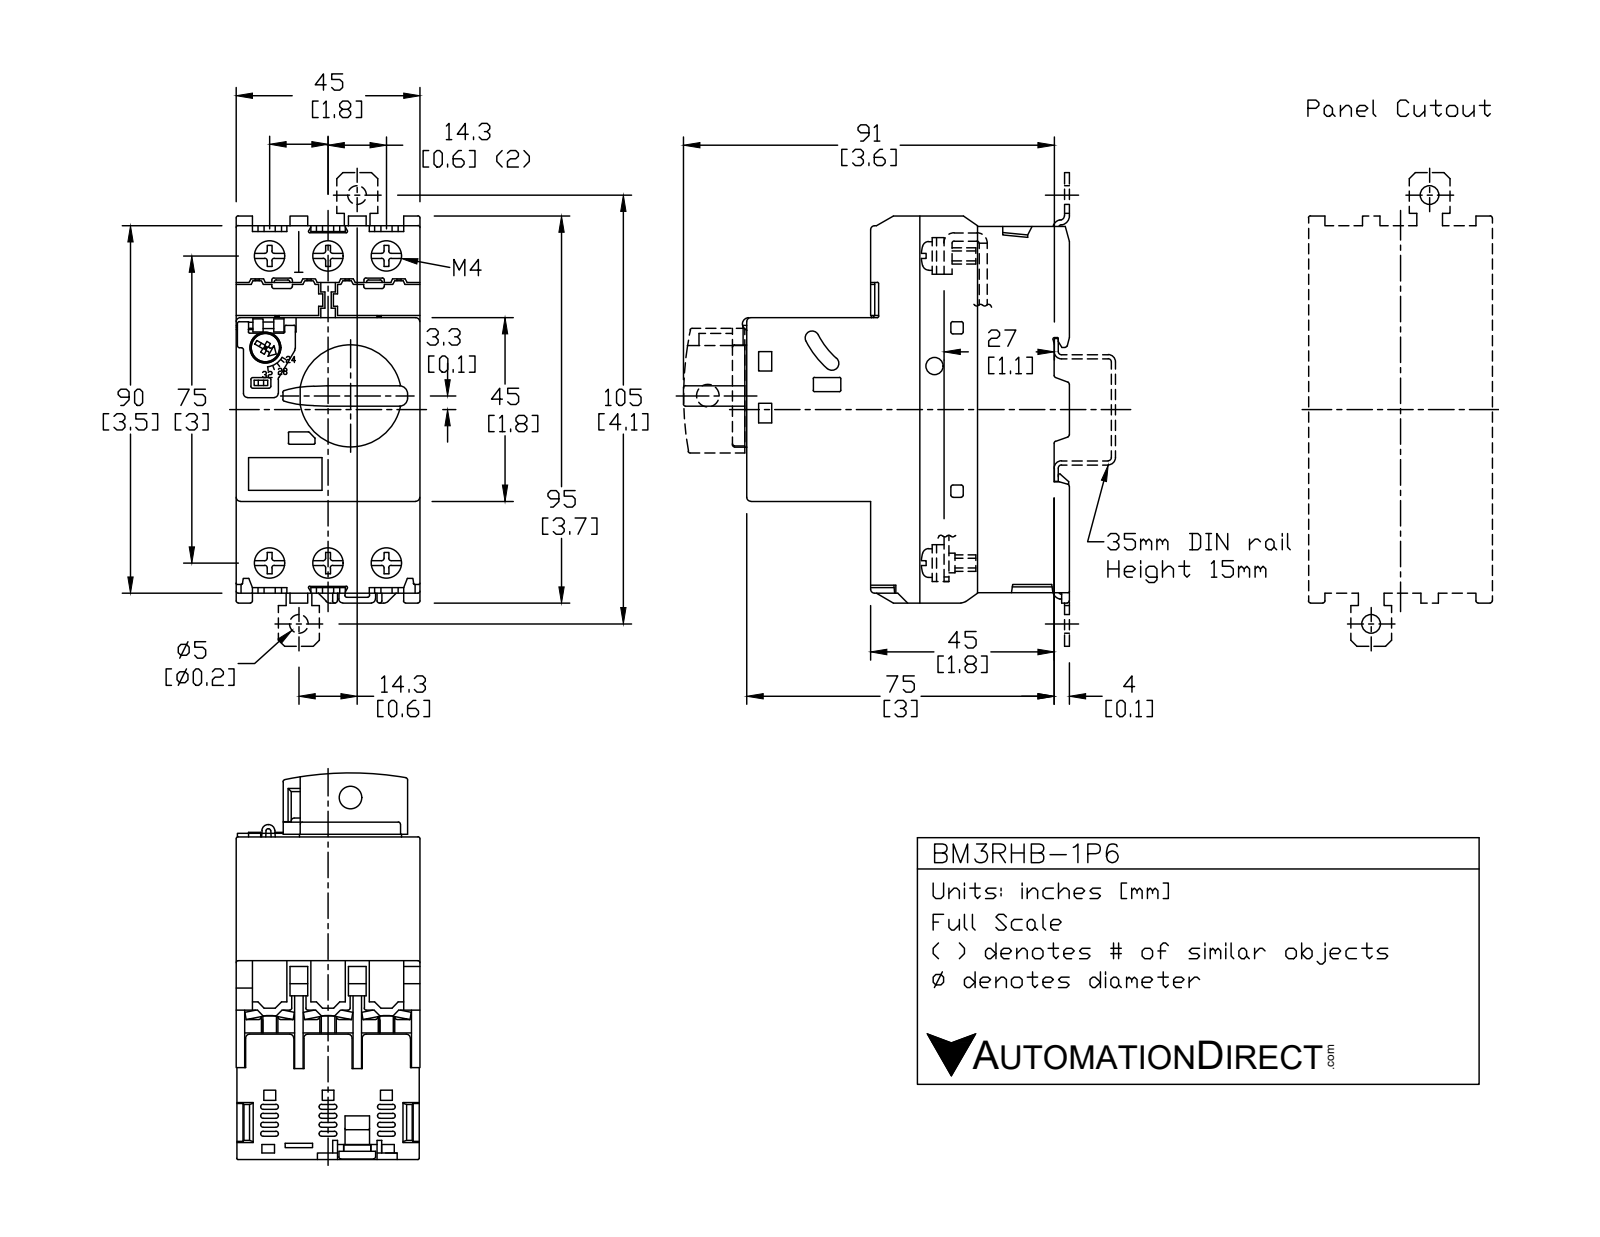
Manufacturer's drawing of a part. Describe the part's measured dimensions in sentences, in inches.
The part is named "BM3RHB-1P6". Its 3-D file was written by "SolidWorks 2018 (AUTOMOTIVE_DESIGN)". It is 25 solids with 1294 faces: 964 planar, 327 cylindrical and 3 other. Overall it measures 3.732 by 3.72 by 1.772 inches. Its volume is 14.13 cubic inches and its surface area 88.41 square inches. Round holes: 6 of diameter 0.157, 6 of diameter 0.291, 1 of diameter 0.063, 1 of diameter 0.165, 1 of diameter 0.197, 1 of diameter 0.217, 1 of diameter 0.295. Round bosses or shafts: 6 of diameter 0.236, 1 of diameter 0.984, 1 of diameter 0.276. Partial cylindrical surfaces (rounded edges, fillets, slot ends): 67 of radius 0.02, 24 of radius 0.024, 14 of radius 0.079, 12 of radius 0.012, 8 of radius 0.039, 8 of radius 0.098, 6 of radius 0.008, 2 of radius 0.059. The main face-to-face distances are 1.772, 1.441, 1.669, 3.11, 0.882, 2.654, 0.118, 0.65, 0.791, 0.472. The hole center spacings are 0.563, 3.006, 2.953, 1.126, 3.16, 0.883, 0.941, 1.068.
